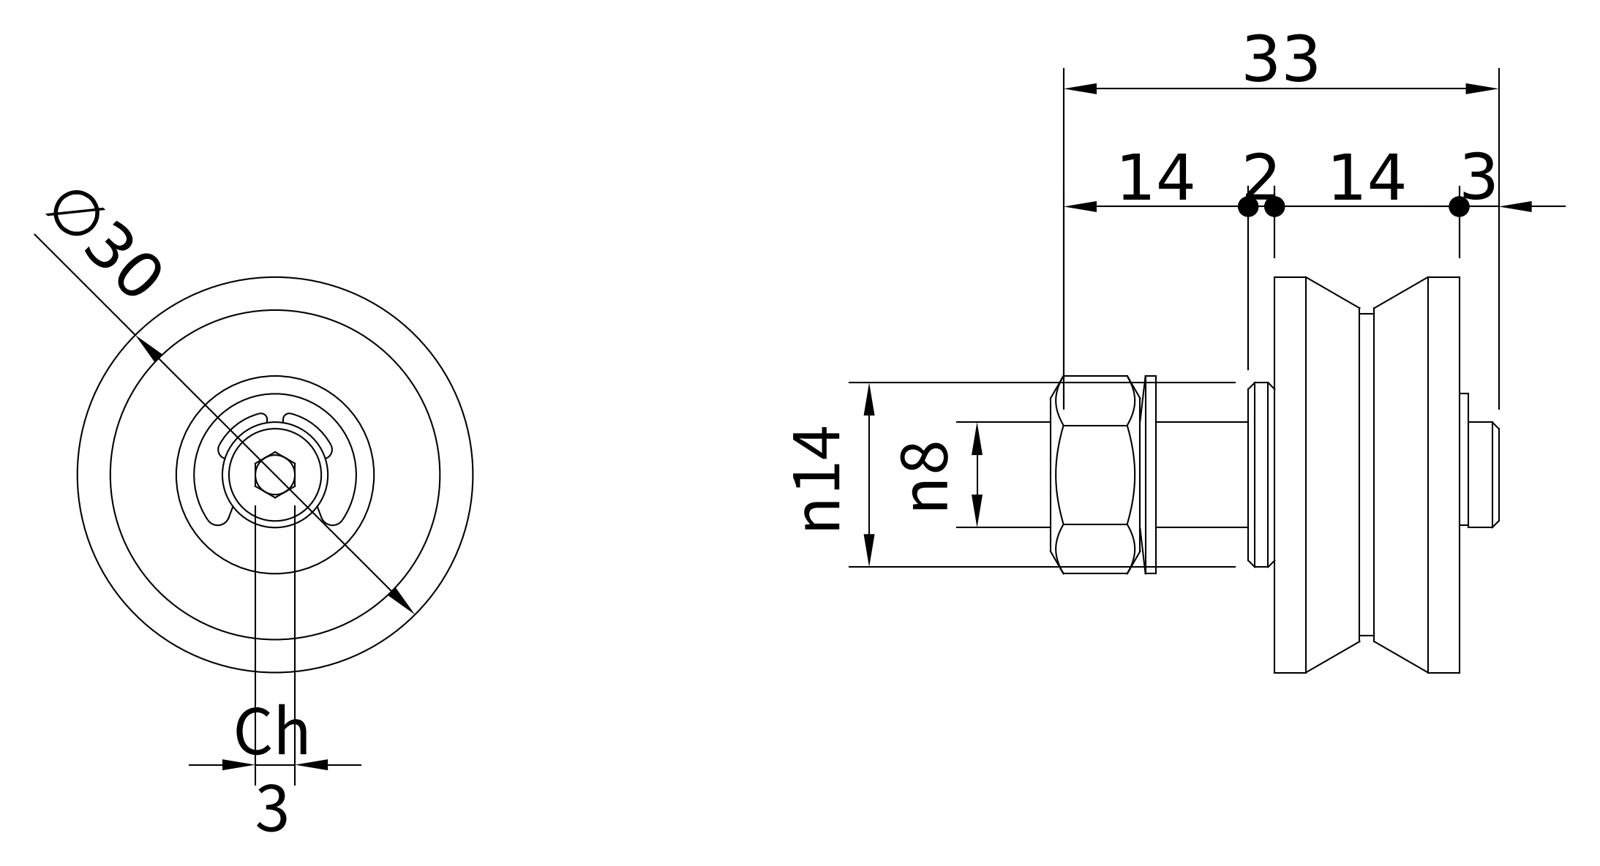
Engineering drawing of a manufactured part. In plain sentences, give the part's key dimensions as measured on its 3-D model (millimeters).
The part is named "23.530.00C; 70PE00132-A; CRUGC0000022; CDDDE0000044 (+2 more)". Its 3-D file was written by "Autodesk Inventor 2022 (AUTOMOTIVE_DESIGN)". It is 5 solids with 100 faces: 54 planar, 32 cylindrical and 14 other. Overall it measures 34 by 30 by 30 millimeters. Its volume is 10 372 cubic millimeters and its surface area 5 546 square millimeters. Round holes: 1 of diameter 3, 1 of diameter 6, 1 of diameter 6.65, 1 of diameter 8.2, 1 of diameter 25. Round bosses or shafts: 1 of diameter 30, 1 of diameter 24.4, 1 of diameter 15, 1 of diameter 14, 1 of diameter 8. Partial cylindrical surfaces (rounded edges, fillets, slot ends): 2 of radius 0.18, 2 of radius 0.48, 2 of radius 0.72, 2 of radius 0.9, 1 of radius 0.6, 1 of radius 4.8, 1 of radius 6.15. The main face-to-face distances are 0.5, 13.5, 13, 14, 16, 17, 2, 2.5, 15.5, 5.
